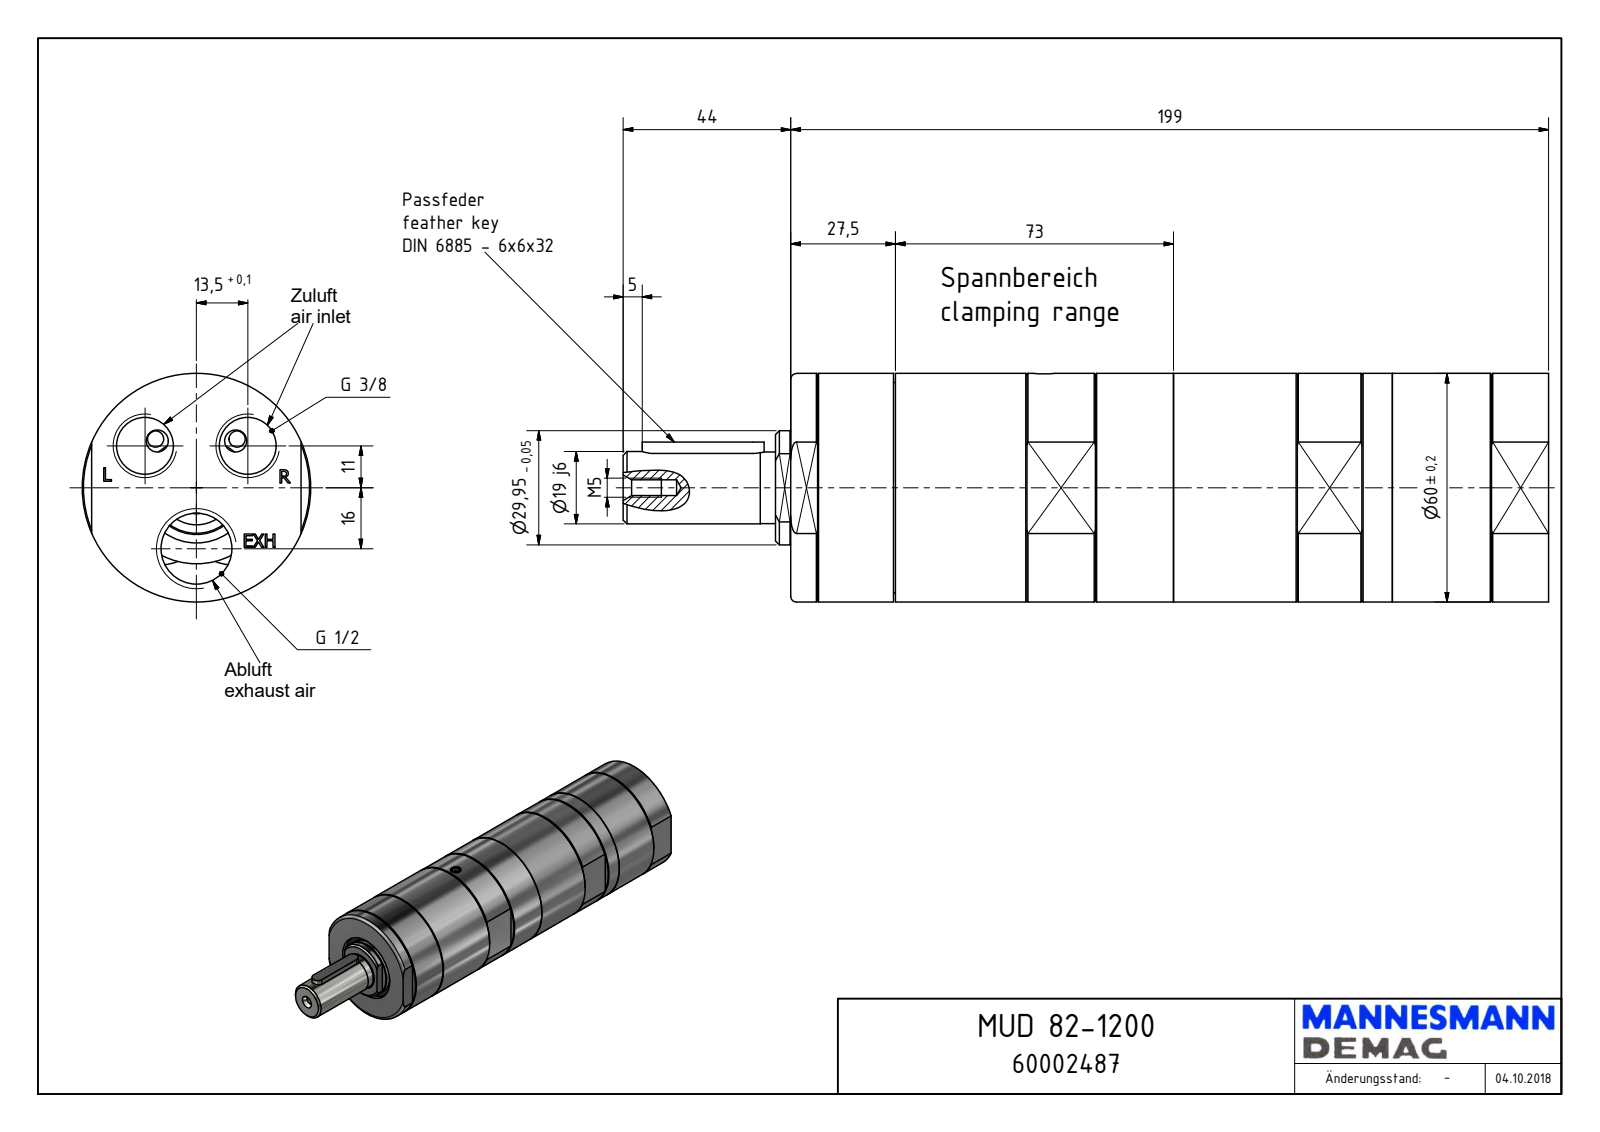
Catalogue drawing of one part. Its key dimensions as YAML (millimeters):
part_name: "MUD 82-1200_60002487"
step_written_by: "Autodesk Inventor 2018 (AUTOMOTIVE_DESIGN)"
units: millimeters
bodies: {solids: 1, faces: 197, planar: 108, cylindrical: 44, other: 45}
overall_size: [243, 60, 60]
volume: 558459
surface_area: 52392
round_holes:
  - {diameter: 14.95, count: 2}
  - {diameter: 1.55, count: 1}
  - {diameter: 4, count: 1}
  - {diameter: 4.13, count: 1}
  - {diameter: 5.5, count: 1}
  - {diameter: 18.63, count: 1}
  - {diameter: 35, count: 1}
  - {diameter: 55.38, count: 1}
round_bosses_or_shafts:
  - {diameter: 60, count: 1}
  - {diameter: 55.18, count: 1}
  - {diameter: 29.95, count: 1}
  - {diameter: 19, count: 1}
  - {diameter: 18.8, count: 1}
  - {diameter: 5, count: 1}
  - {diameter: 3.6, count: 1}
partial_cylinders:
  - {radius: 3, count: 2}
  - {radius: 7.5, count: 2}
  - {radius: 8.5, count: 1}
  - {radius: 19.11, count: 1}
  - {radius: 23.5, count: 1}
  - {radius: 25.47, count: 1}
face_to_face_distances: [199, 55, 183.14, 15.86, 186, 2.86, 13, 158.5, 27.5, 155.64]
hole_center_spacings: [17.41, 30.19, 16, 27]
